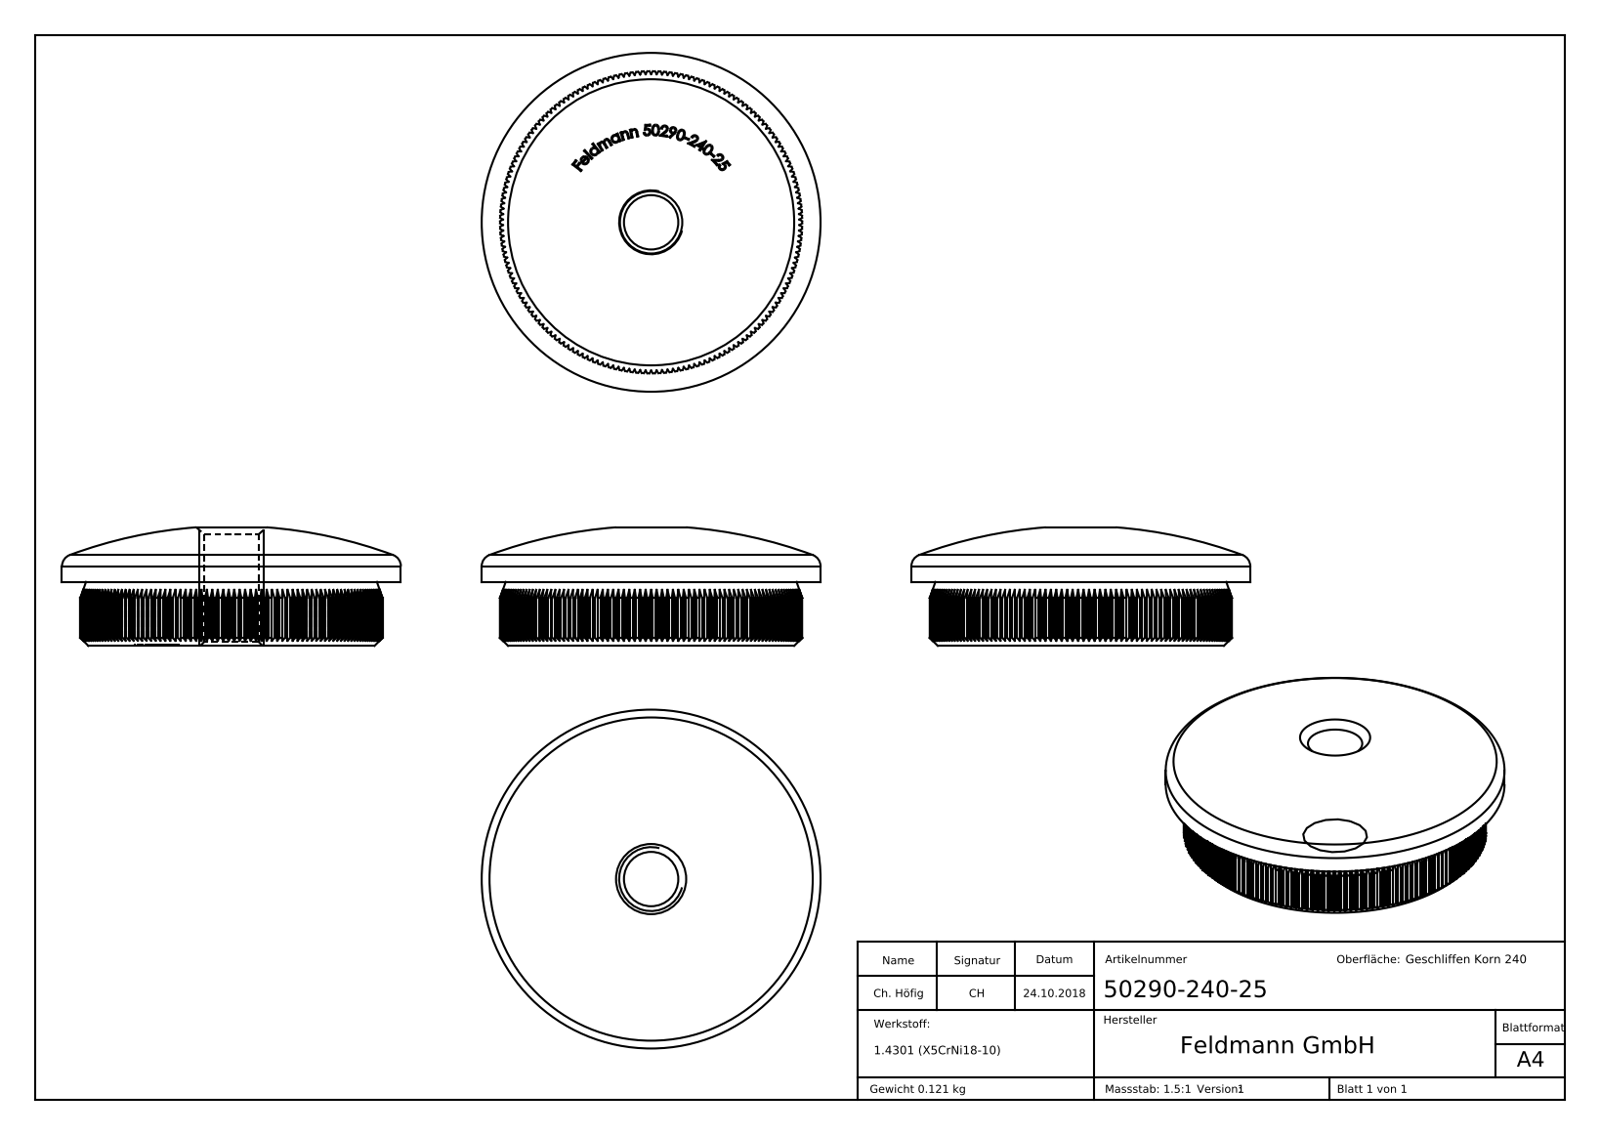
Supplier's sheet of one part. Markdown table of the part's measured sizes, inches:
| quantity | value |
| --- | --- |
| part name | 50290-240-25 |
| STEP written by | SolidWorks 2015 (CONFIG_CONTROL_DESIGN) |
| units | inches |
| bodies | 1 solid, 753 faces (472 planar, 174 cylindrical, 107 other) |
| overall size | 1.669 × 1.669 × 0.584 |
| volume | 0.933 in³ |
| surface area | 7.483 in² |
| round holes (diameter × count) | 0.268 × 1 |
| round bosses / shafts (diameter × count) | 1.669 × 1 |
| partial cylindrical surfaces (radius × count) | 0.744 × 1 |
| main face-to-face distances | 0.315, 0.731, 0.73, 0.731, 0.311, 0.729, 0.026, 0.021, 0.026, 0.031 |
